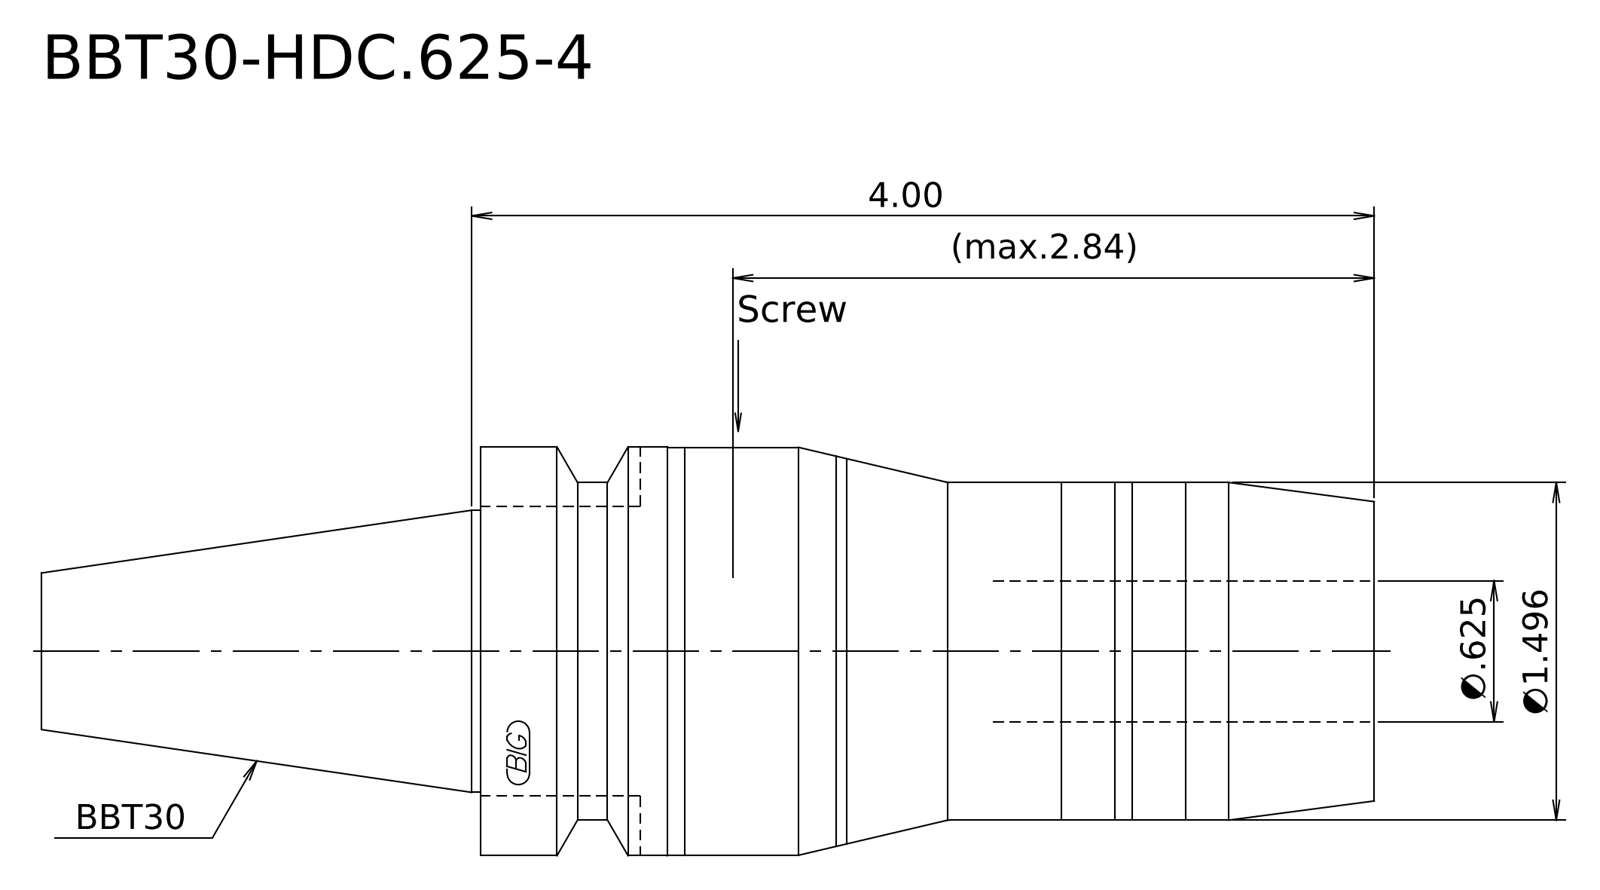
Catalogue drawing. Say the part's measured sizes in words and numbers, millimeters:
Its 3-D file was written by "Kubotek KeyCreator 2011 V10.0.2 (22737) (automotive_design)". It is 1 solid with 15 faces: 3 planar, 6 cylindrical and 6 other. Overall it measures 150 by 46 by 46 millimeters. Its volume is 156 647 cubic millimeters and its surface area 19 448 square millimeters. Round bosses or shafts: 1 of diameter 46, 1 of diameter 45.9, 1 of diameter 38, 1 of diameter 31.75. The main face-to-face distances are 100.6, 150, 49.4.
